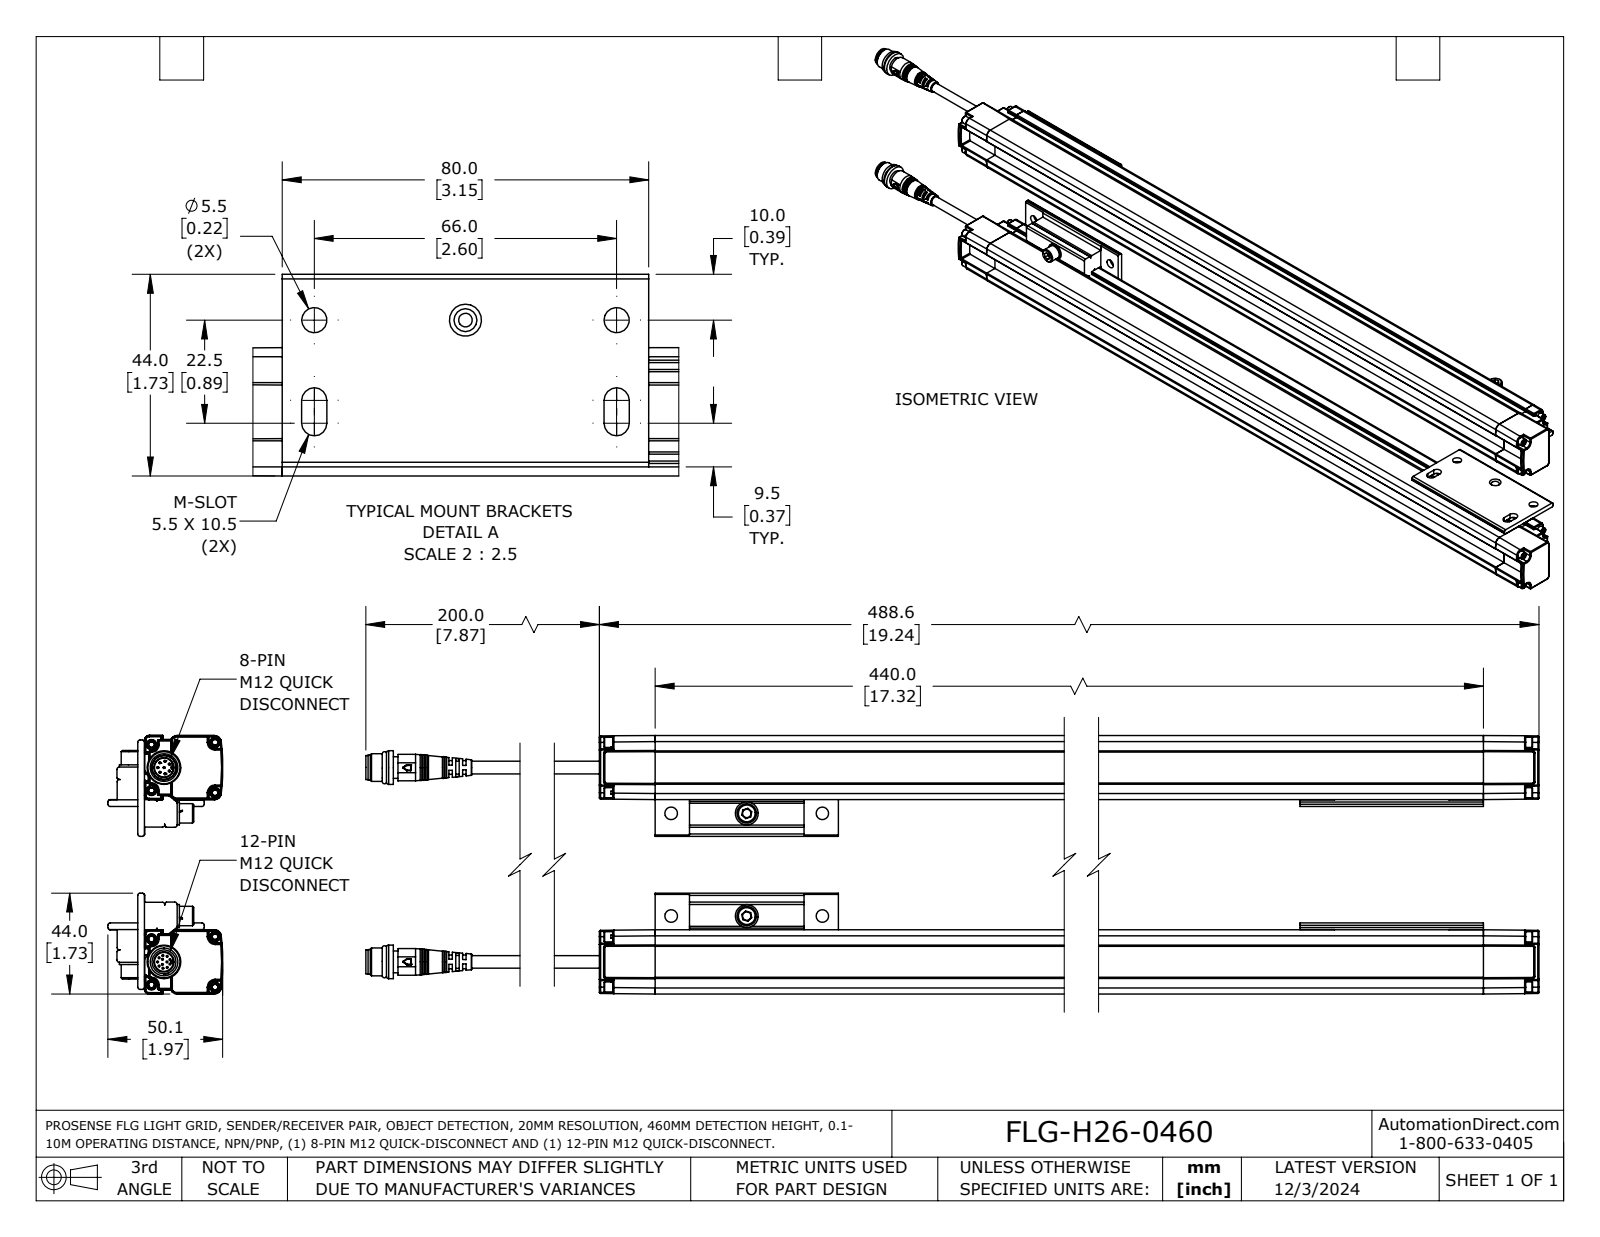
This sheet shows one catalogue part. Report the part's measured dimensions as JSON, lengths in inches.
{"part_name": "FLG-H26-0460", "step_written_by": "SolidWorks 2023 (AUTOMOTIVE_DESIGN)", "units": "inches", "bodies": {"solids": 10, "faces": 1632, "planar": 804, "cylindrical": 444, "other": 384}, "overall_size": [22.856, 4.441, 1.972], "volume_in3": 50.64, "surface_area_in2": 355.2, "round_holes": [[0.016, 16], [0.217, 6], [0.098, 4], [0.197, 3], [0.327, 2]], "round_bosses_or_shafts": [[0.177, 8], [0.118, 8], [0.031, 8], [0.217, 4], [0.059, 4], [0.394, 3], [0.335, 3], [0.146, 3]], "partial_cylinders_radius": [[0.02, 142], [0.039, 40], [0.01, 20], [0.008, 12], [0.012, 12], [0.108, 12], [0.1, 6], [0.049, 4]], "face_to_face_distances": [3.339, 1.102, 0.071, 0.285, 0.817, 0.118, 2.236, 0.97, 1.041, 4.441], "hole_center_spacings": [0.108, 1.299, 0.163, 0.979, 2.191, 0.215, 1.764, 2.598]}
